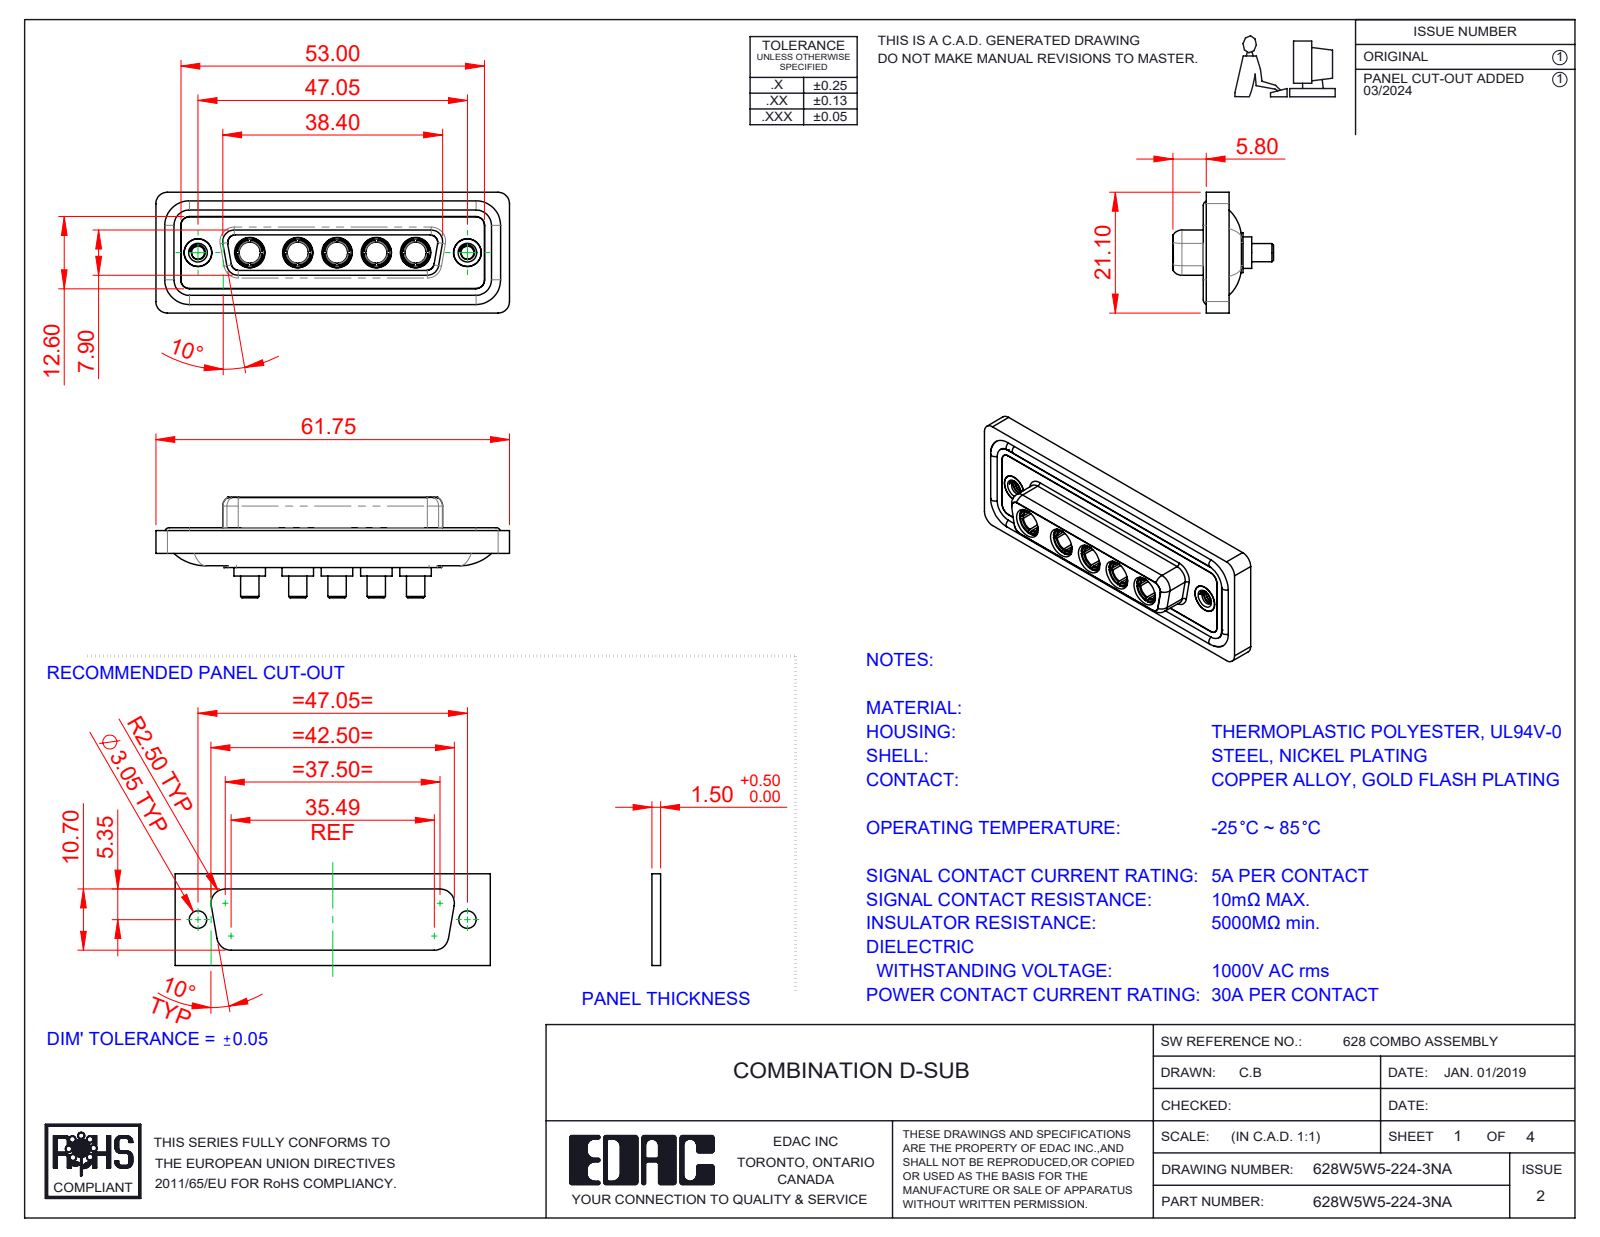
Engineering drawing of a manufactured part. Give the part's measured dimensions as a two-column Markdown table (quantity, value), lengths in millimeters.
| quantity | value |
| --- | --- |
| part name | Power Socket_30A S; 628Combo Threaded Rivet_A; 628Combo Shell Front_25 Contacts; 628Combo Housing_5W5 (+3 more) |
| STEP written by | SolidWorks 2023 (CONFIG_CONTROL_DESIGN) |
| units | millimeters |
| bodies | 17 solids, 754 faces (250 planar, 305 cylindrical, 199 other) |
| overall size | 61.75 × 21.1 × 17.55 |
| volume | 8 210 mm³ |
| surface area | 13 436 mm² |
| round holes (diameter × count) | 4.85 × 7, 3.7 × 5, 5.3 × 5, 2.26 × 2, 4 × 2, 4.05 × 2, 5 × 2 |
| round bosses / shafts (diameter × count) | 5.5 × 5, 5.2 × 5, 4.96 × 5, 4.75 × 5, 3.75 × 5, 3.2 × 5, 1.6 × 4, 4.95 × 2 |
| partial cylindrical surfaces (radius × count) | 1.5 × 22, 2 × 18, 1.35 × 8, 1.6 × 8, 2.1 × 5, 0.25 × 4, 0.5 × 4, 0.6 × 4 |
| main face-to-face distances | 0.4, 1.8, 7.45, 5.65, 0.5, 7.05, 6.6, 1.6, 1.1, 2.9 |
| hole center spacings | 6.86, 9.04, 13.72, 38.01, 8.39, 15.25, 15.9, 17.43 |
